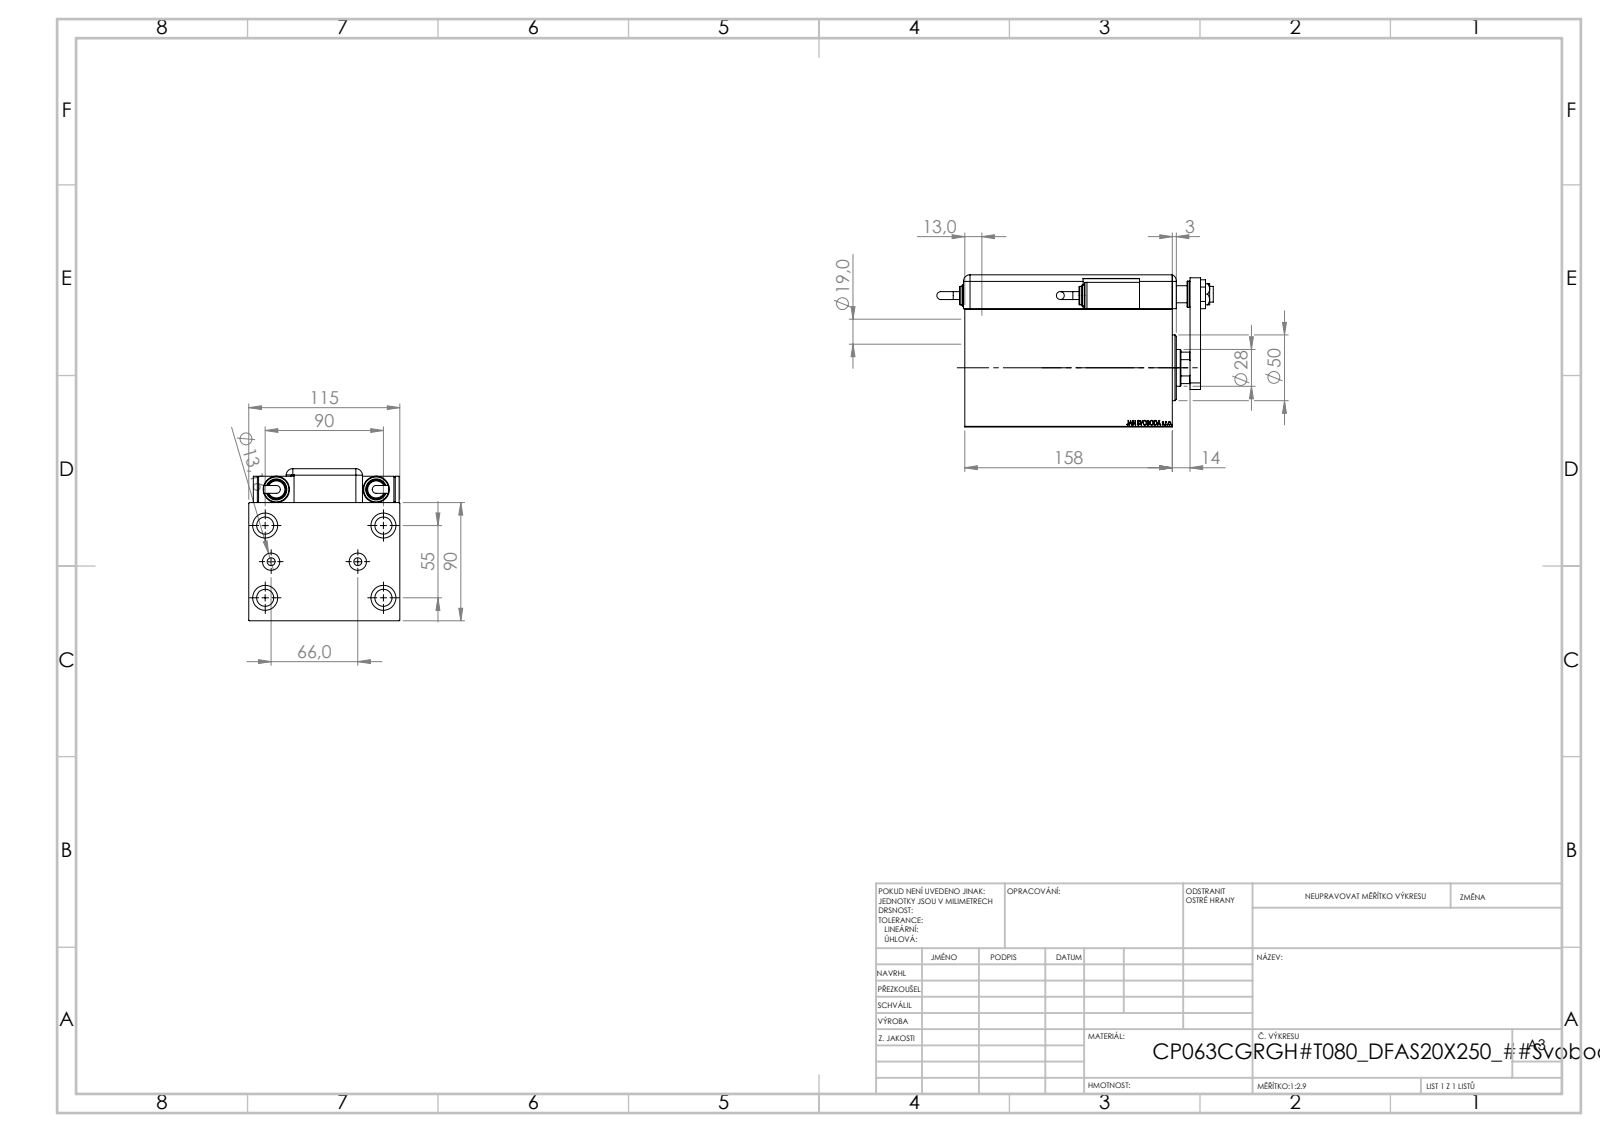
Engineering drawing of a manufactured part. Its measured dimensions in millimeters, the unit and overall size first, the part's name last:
Units: millimetres
Overall size (bounding box): 210.46 × 115.8 × 115
Round holes (diameter × count): ⌀13 ×5, ⌀19 ×4, ⌀4 ×2, ⌀6 ×2, ⌀8 ×2, ⌀13.16 ×2, ⌀12 ×1, ⌀14 ×1, ⌀18.5 ×1, ⌀20 ×1, ⌀28 ×1, ⌀31.5 ×1
Round bosses / shafts (diameter × count): ⌀20 ×3, ⌀16 ×2, ⌀14 ×2, ⌀6 ×2, ⌀50 ×1
Partial cylindrical surfaces — rounded edges, fillets, slot ends (radius × count): R5 ×9, R10 ×1, R13.5 ×1
Main face-to-face distances: 90, 115, 3, 158, 25.8, 115.8, 17.5, 140.5, 28.5, 112.8
Hole centre spacings: 52.74, 53.27, 27.87, 33.71, 52.22, 55, 75.67, 89.81
Volume: 1 504 000 mm³ · Surface area: 251 434 mm²
Bodies: 13 solids, 1244 faces (614 planar, 113 cylindrical, 517 other)
Part name (STEP PRODUCT): SWITCH Q; TYC; SWITCH DIM A_G; NUT_D19 (+7 more)
STEP written by: SolidWorks 2019 (CONFIG_CONTROL_DESIGN)
